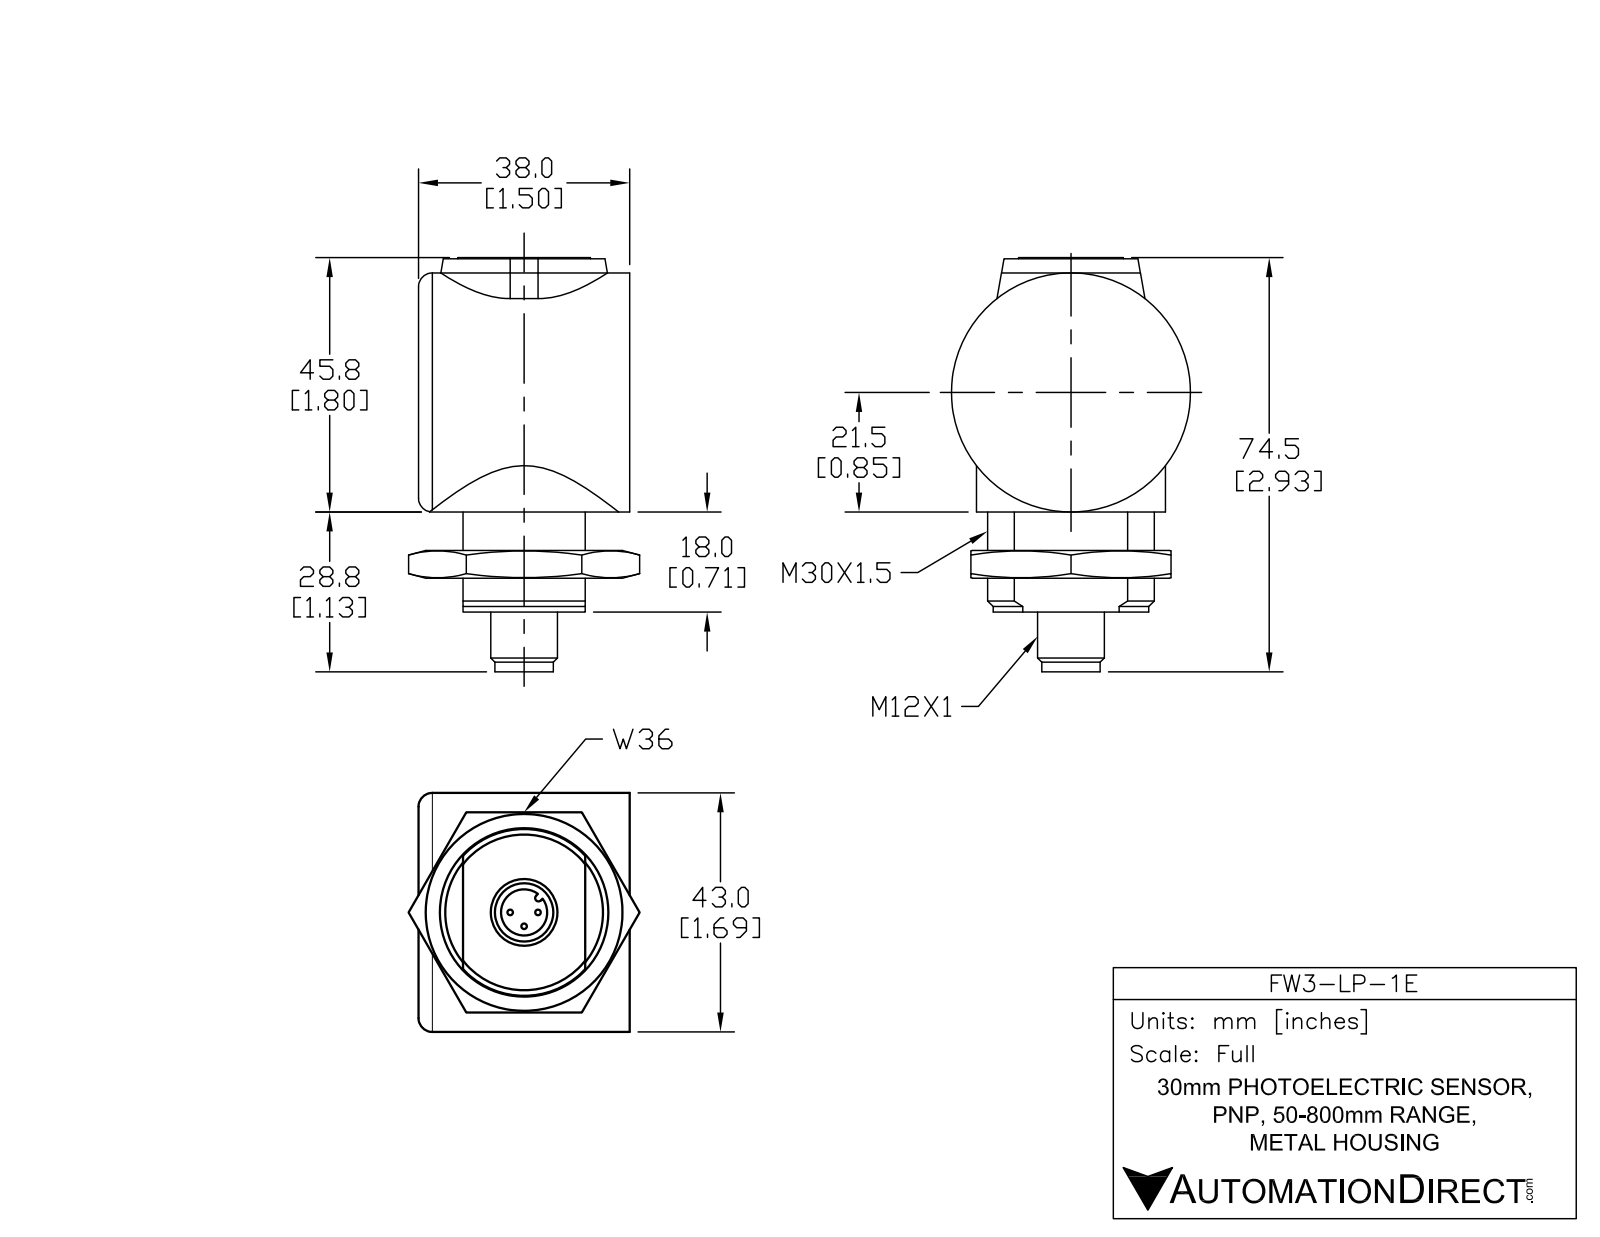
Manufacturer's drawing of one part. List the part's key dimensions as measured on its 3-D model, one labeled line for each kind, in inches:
Part name (STEP PRODUCT): FW3-LP-1E
STEP written by: SolidWorks 2013 (AUTOMOTIVE_DESIGN)
Units: inches
Bodies: 1 solid, 201 faces (111 planar, 35 cylindrical, 55 other)
Overall size (bounding box): 2.928 × 1.69 × 1.49
Volume: 4.301 in³ · Surface area: 19.68 in²
Round holes (diameter × count): ⌀0.172 ×1, ⌀0.315 ×1, ⌀1.58 ×1
Round bosses / shafts (diameter × count): ⌀0.04 ×3, ⌀1.69 ×1, ⌀0.47 ×1, ⌀0.39 ×1, ⌀0.18 ×1
Partial cylindrical surfaces — rounded edges, fillets, slot ends (radius × count): R0.48 ×2, R0.64 ×2, R0.025 ×1, R0.408 ×1, R0.492 ×1, R0.545 ×1, R0.587 ×1
Main face-to-face distances: 1.44, 2.498, 0.11, 2.388, 0.3, 0.19, 2.198, 1.178, 0.262, 0.312
Hole centre spacings: 0.349
